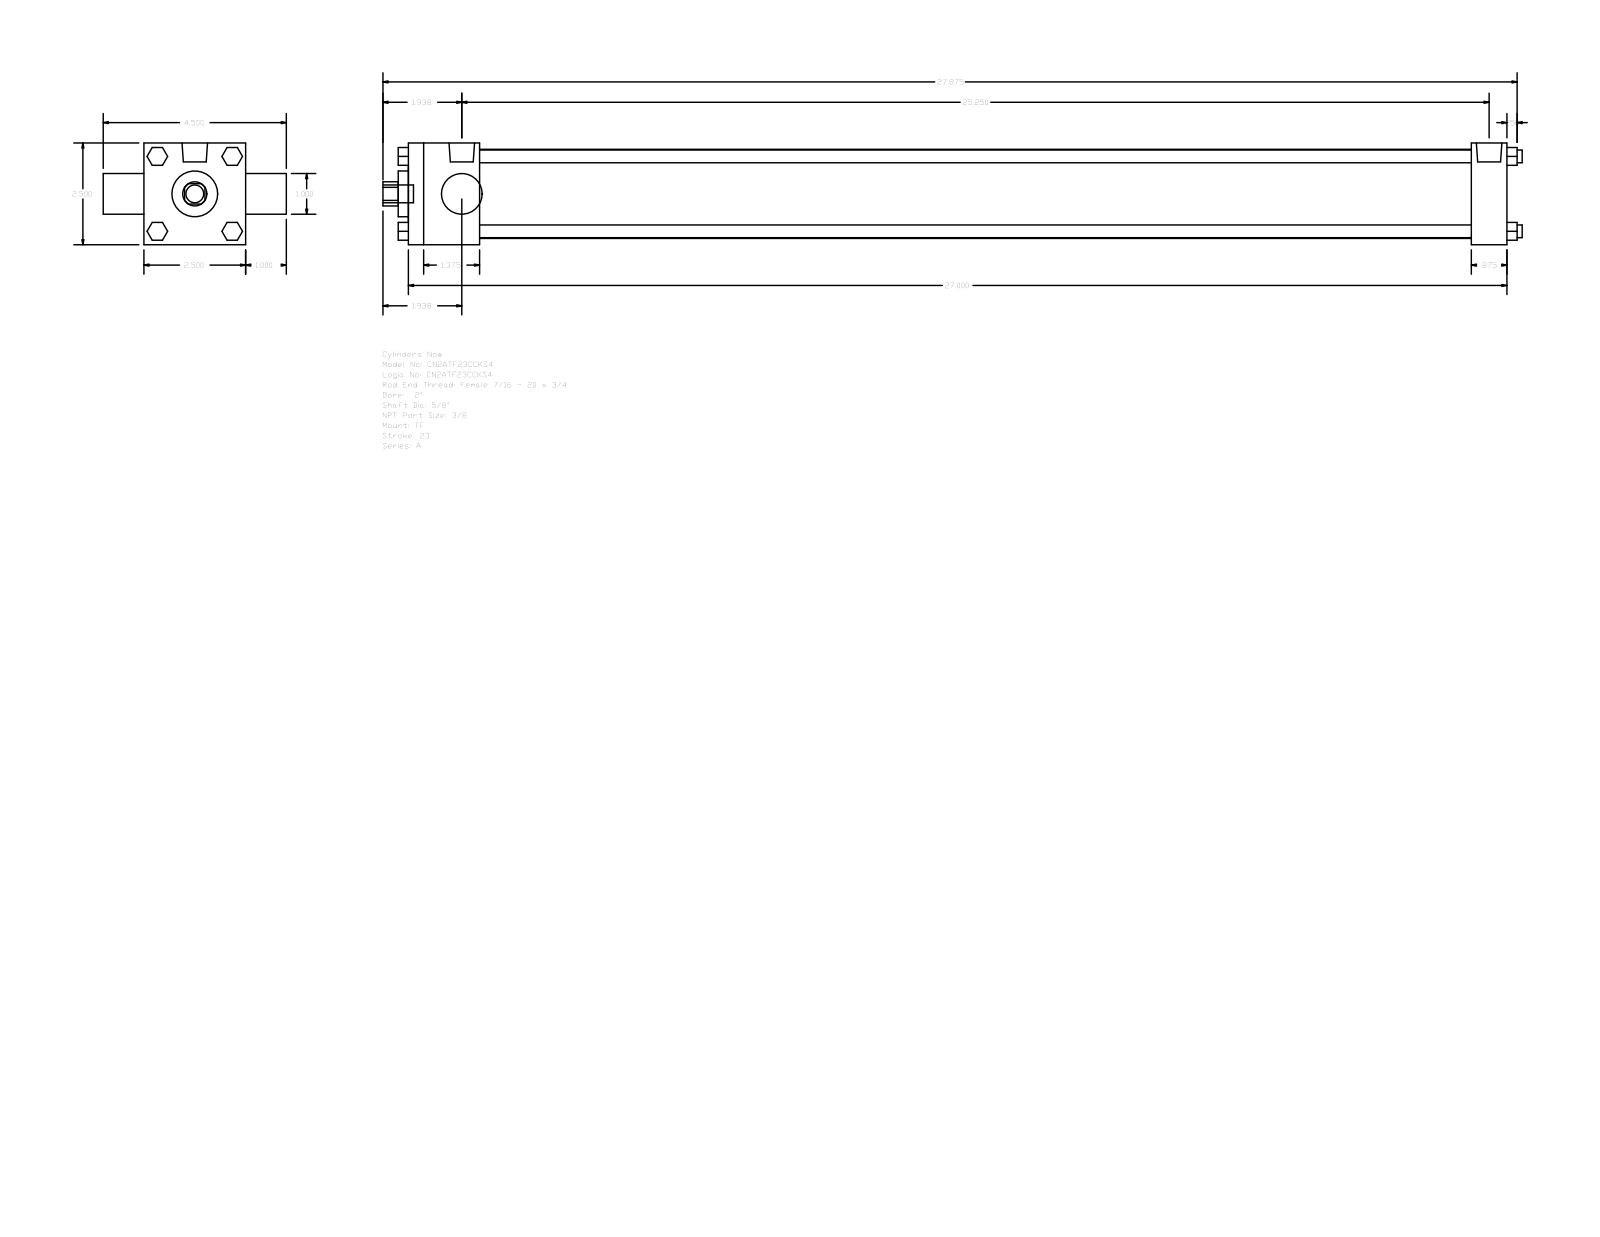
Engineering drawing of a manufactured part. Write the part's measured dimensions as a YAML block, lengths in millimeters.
part_name: "A_TF__0200_0.625"
step_written_by: "GSSL Pune (CONFIG_CONTROL_DESIGN)"
units: millimeters
bodies: {solids: 0, faces: 120, planar: 92, cylindrical: 28, other: 0}
overall_size: [711.2, 114.3, 63.5]
round_holes:
  - {diameter: 15.88, count: 1}
  - {diameter: 25.4, count: 1}
  - {diameter: 28.57, count: 1}
  - {diameter: 55.63, count: 1}
round_bosses_or_shafts:
  - {diameter: 7.94, count: 4}
  - {diameter: 5.56, count: 3}
  - {diameter: 15.93, count: 2}
  - {diameter: 11.11, count: 1}
partial_cylinders:
  - {radius: 7.54, count: 1}
face_to_face_distances: [63.5, 685.79, 44.45, 663.57, 619.12, 641.34, 22.22, 25.4, 88.9, 6.35]
